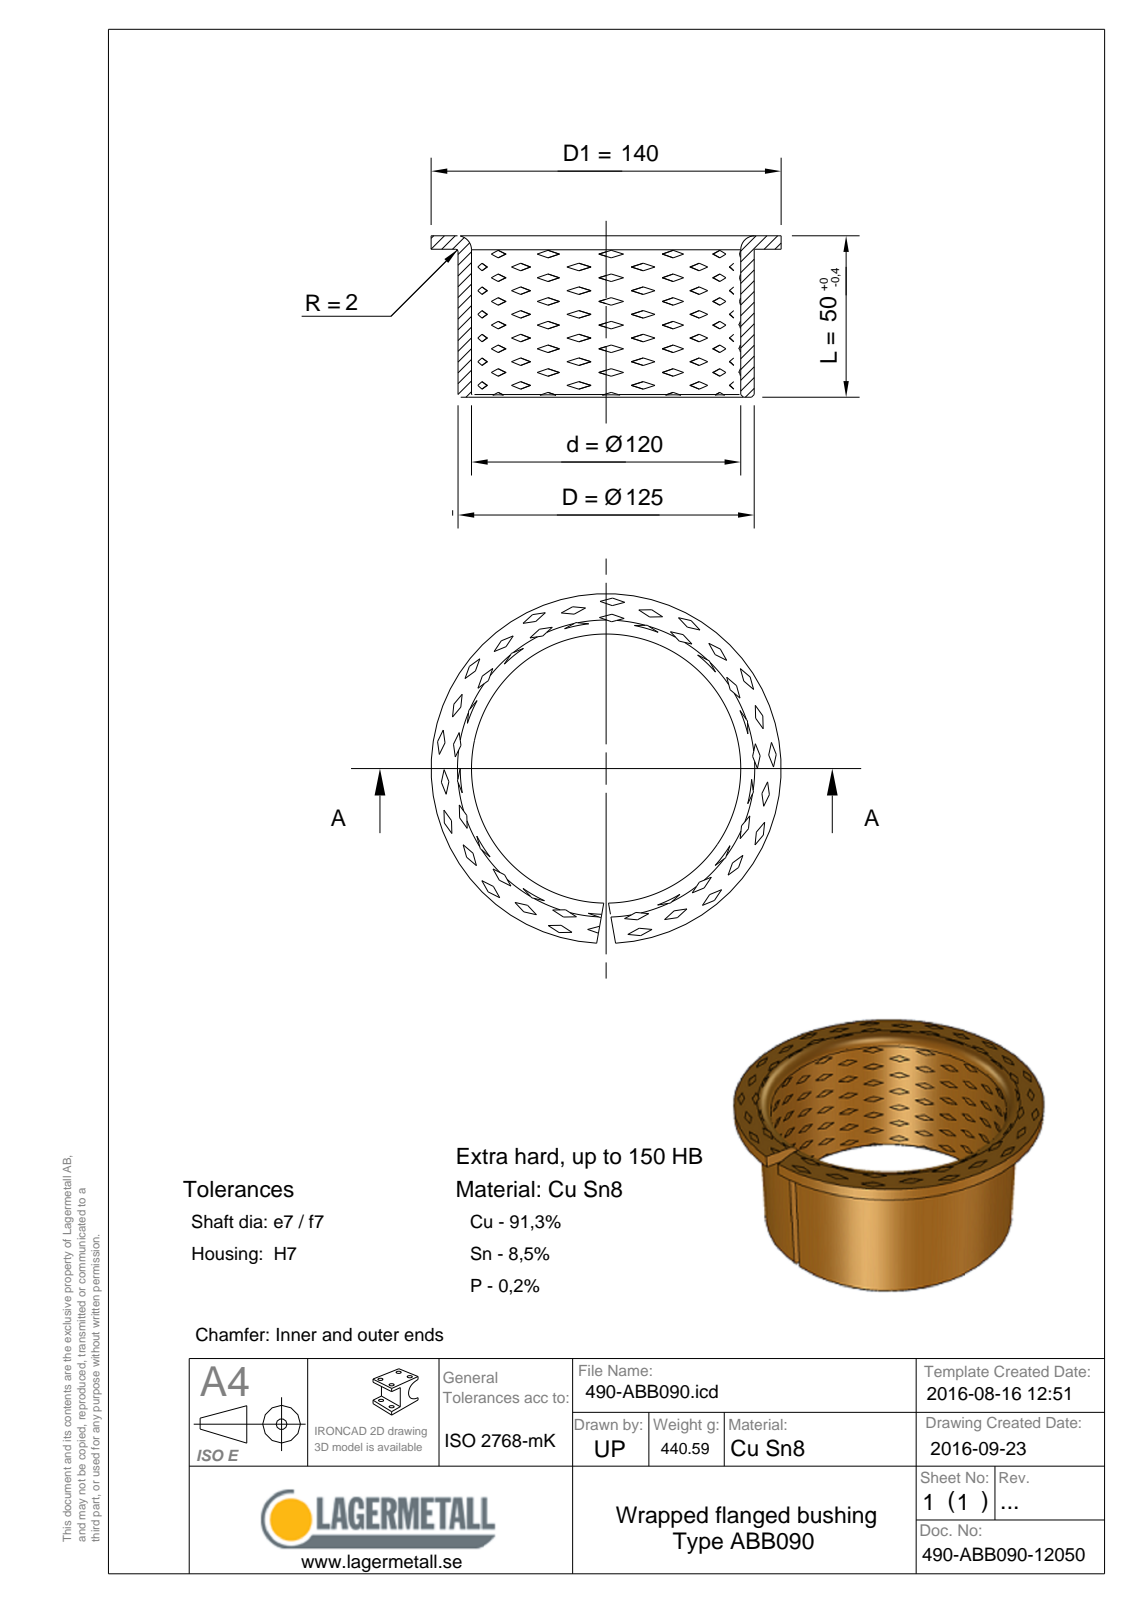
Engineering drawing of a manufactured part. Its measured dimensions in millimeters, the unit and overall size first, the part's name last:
Units: millimetres
Overall size (bounding box): 140 × 140 × 50
Round holes (diameter × count): ⌀120 ×1
Round bosses / shafts (diameter × count): ⌀140 ×1, ⌀125 ×1
Main face-to-face distances: 2.5, 47.5, 50
Volume: 54 392 mm³ · Surface area: 45 689 mm²
Bodies: 1 solid, 26 faces (5 planar, 9 cylindrical, 12 other)
STEP written by: Spatial InterOp 3D (CONFIG_CONTROL_DESIGN)
